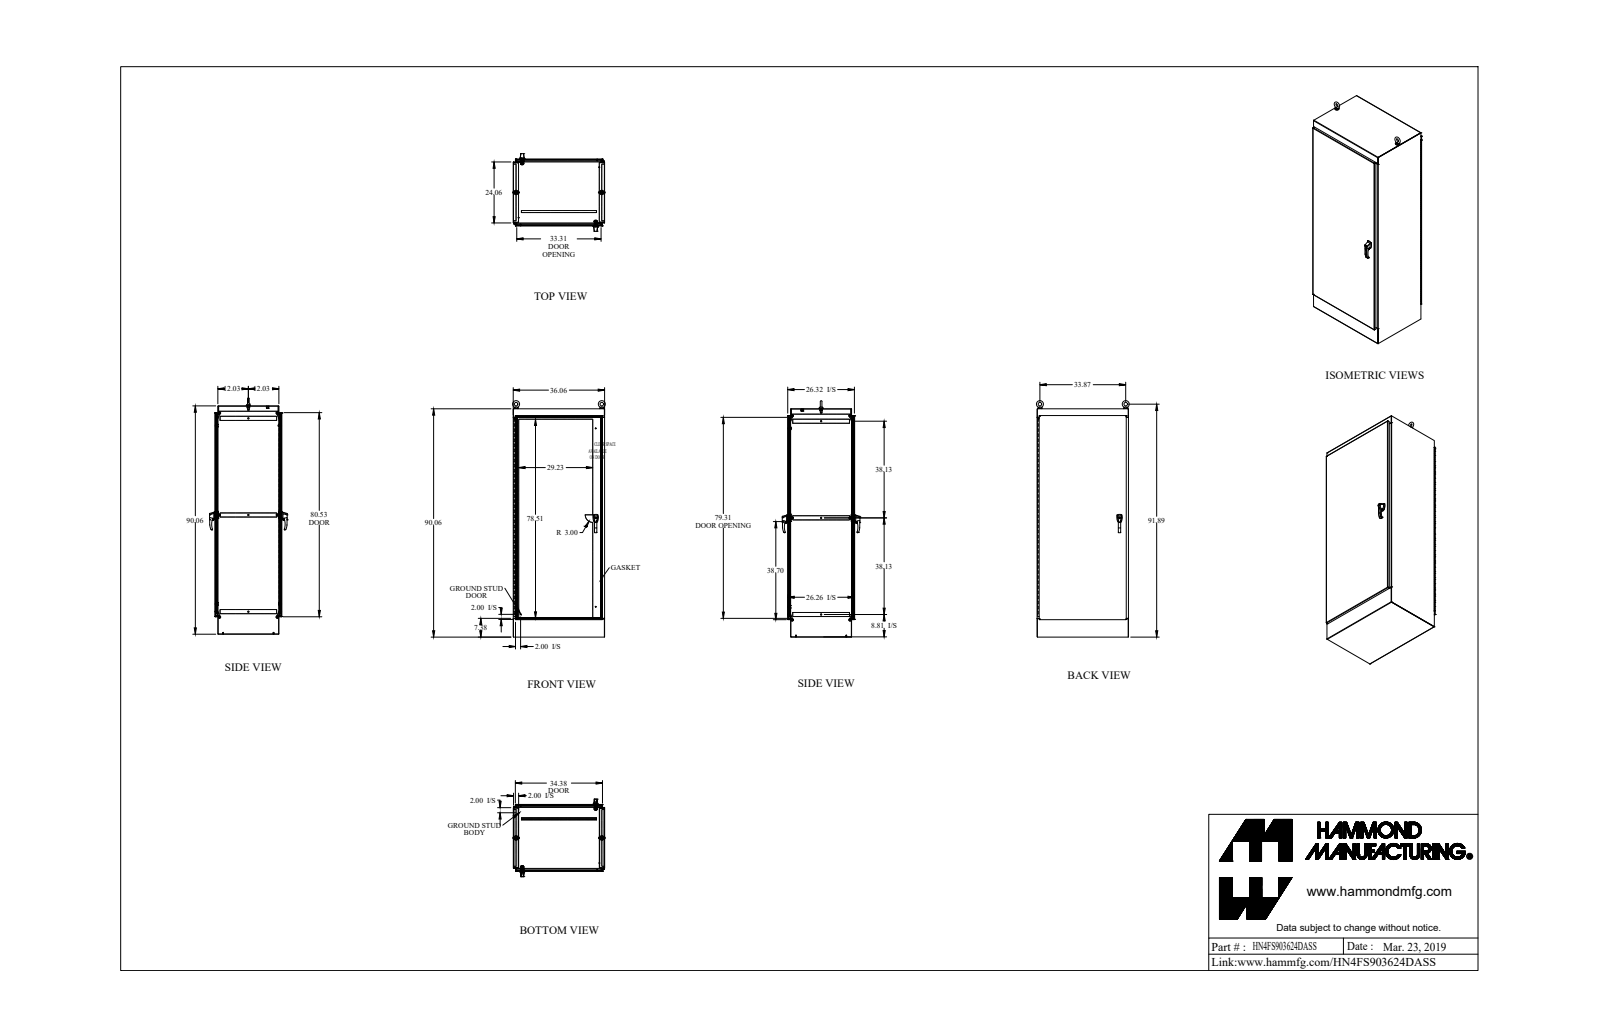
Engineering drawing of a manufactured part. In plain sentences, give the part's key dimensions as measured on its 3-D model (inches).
The part is named "HN4FS903624DASS". Its 3-D file was written by "SolidWorks 2018 (AUTOMOTIVE_DESIGN)". It is 85 solids with 3529 faces: 1566 planar, 1695 cylindrical and 268 other. Overall it measures 93.489 by 36.604 by 30.664 inches. Its volume is 1 507 cubic inches and its surface area 31 926 square inches. Round holes: 26 of diameter 0.304, 8 of diameter 0.35, 4 of diameter 0.25, 4 of diameter 0.257, 4 of diameter 0.28, 4 of diameter 0.281, 4 of diameter 0.313, 4 of diameter 0.39, 4 of diameter 0.413, 3 of diameter 0.5, 2 of diameter 0.11, 2 of diameter 0.173. Round bosses or shafts: 4 of diameter 1, 4 of diameter 0.75, 4 of diameter 0.63, 4 of diameter 0.625, 4 of diameter 0.44, 4 of diameter 0.37, 4 of diameter 0.313, 4 of diameter 0.281. Partial cylindrical surfaces (rounded edges, fillets, slot ends): 44 of radius 0.125, 42 of radius 0.043, 36 of radius 0.138, 32 of radius 0.018, 26 of radius 0.048, 26 of radius 0.143, 26 of radius 0.5, 21 of radius 0.06. The main face-to-face distances are 0.095, 26.339, 35.965, 26.244, 26.434, 35.87, 1.187, 25.152, 36.06, 89.965. The hole center spacings are 6, 12, 34.849, 18, 36.365, 38.761, 24, 41.886.
